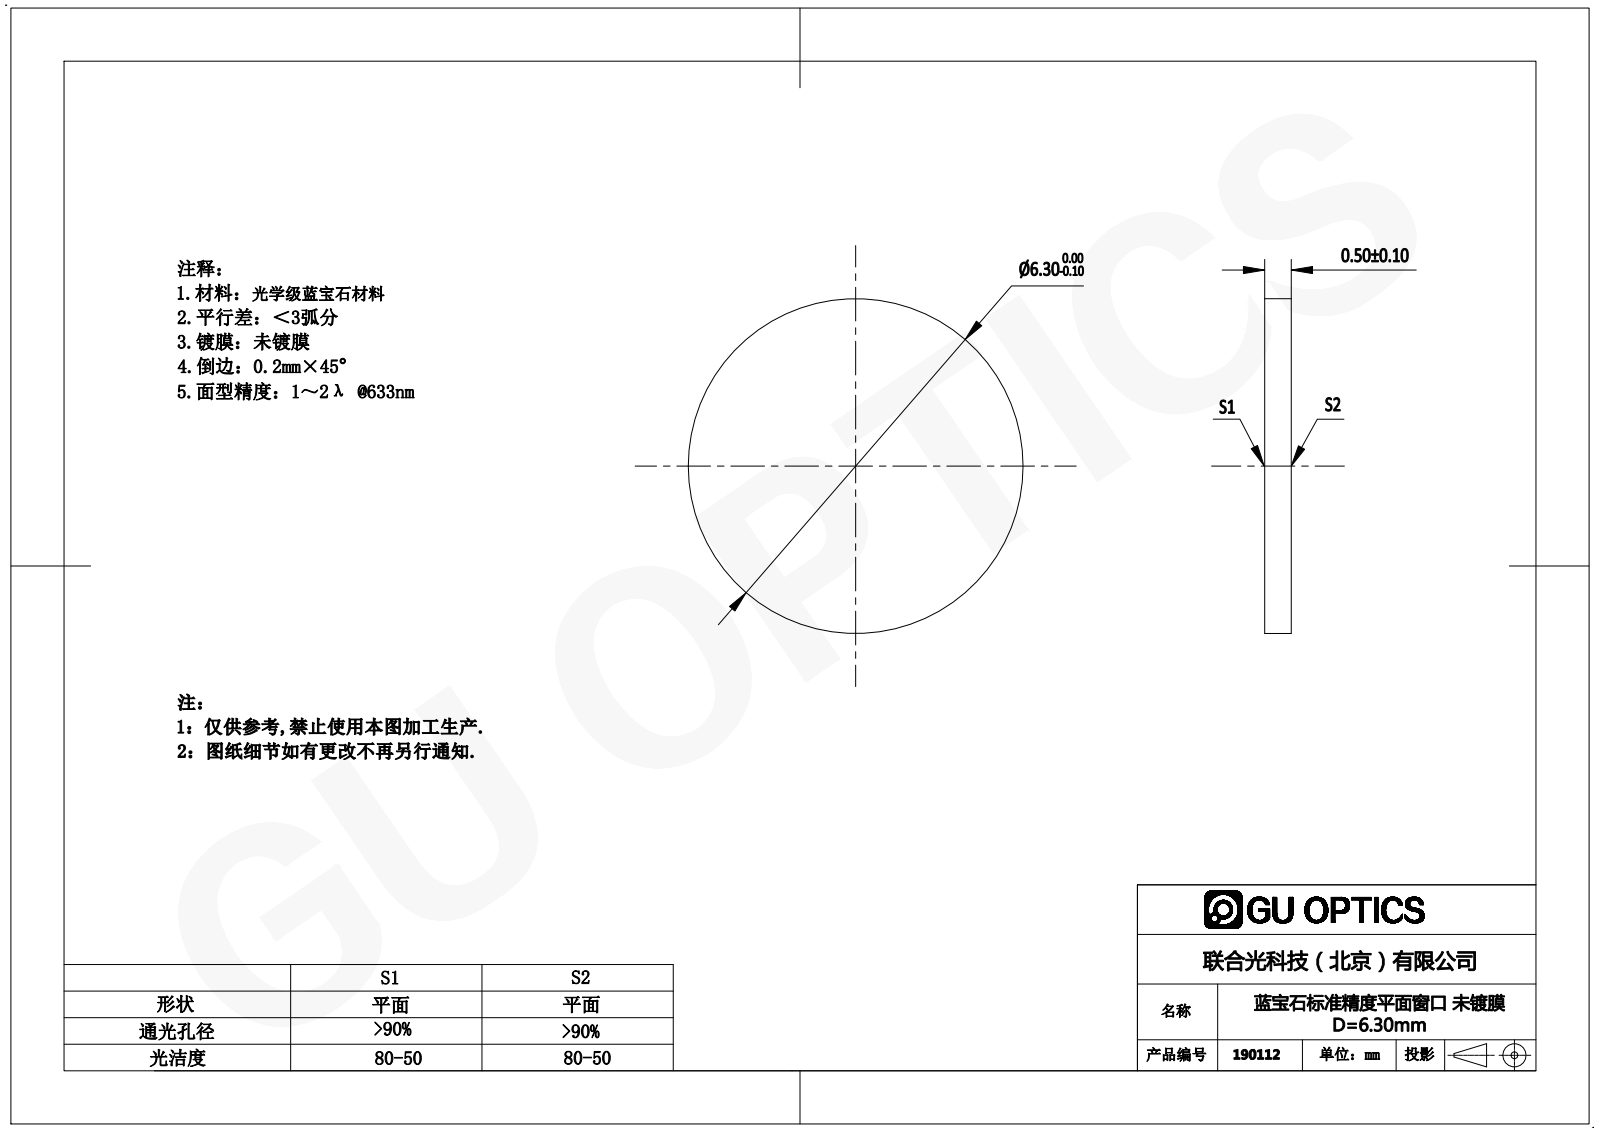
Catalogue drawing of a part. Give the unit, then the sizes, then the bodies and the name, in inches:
Units: inches
Overall size (bounding box): 0.248 × 0.248 × 0.02
Round bosses / shafts (diameter × count): ⌀0.248 ×1
Main face-to-face distances: 0.02
Volume: 0.001 in³ · Surface area: 0.11 in²
Bodies: 1 solid, 4 faces (2 planar, 2 cylindrical, 0 other)
Part name (STEP PRODUCT): 190112
STEP written by: SolidWorks 2016 (AUTOMOTIVE_DESIGN)
